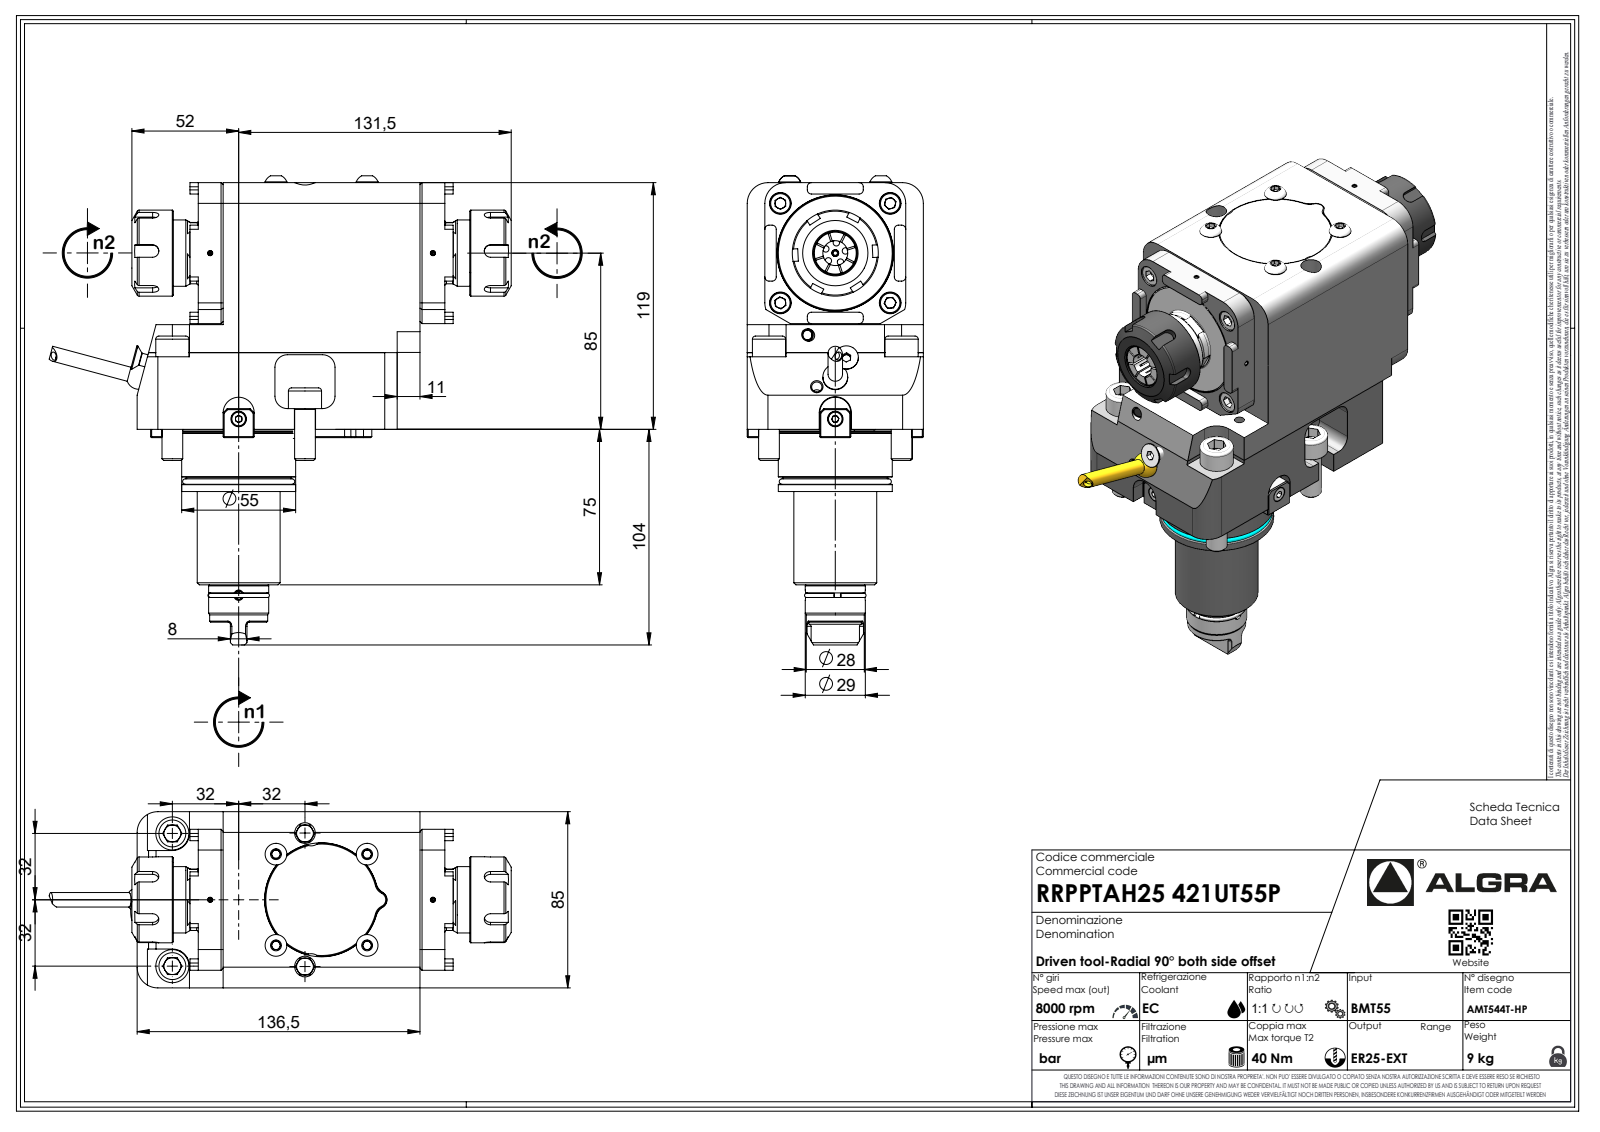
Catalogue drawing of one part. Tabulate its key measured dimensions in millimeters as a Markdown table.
| quantity | value |
| --- | --- |
| part name | RRPPTAH25421UT55P |
| STEP written by | SolidWorks 2023 (AUTOMOTIVE_DESIGN) |
| units | millimeters |
| bodies | 2 solids, 888 faces (571 planar, 162 cylindrical, 155 other) |
| overall size | 223 × 222.98 × 85 |
| volume | 1 261 000 mm³ |
| surface area | 111 470 mm² |
| round holes (diameter × count) | 6 × 2, 10.5 × 2, 2.1 × 1, 4 × 1, 5 × 1, 8.8 × 1, 12 × 1 |
| round bosses / shafts (diameter × count) | 16 × 2, 10 × 2, 62.25 × 1, 55 × 1, 54.6 × 1, 50.2 × 1, 41.5 × 1, 40 × 1 |
| partial cylindrical surfaces (radius × count) | 2 × 23, 3 × 12, 10 × 10, 0.33 × 7, 0.52 × 7, 3.7 × 7, 4 × 6, 6 × 4 |
| main face-to-face distances | 85, 119, 23, 12, 11, 107, 66, 30, 8.5, 68 |
| hole center spacings | 61 |
